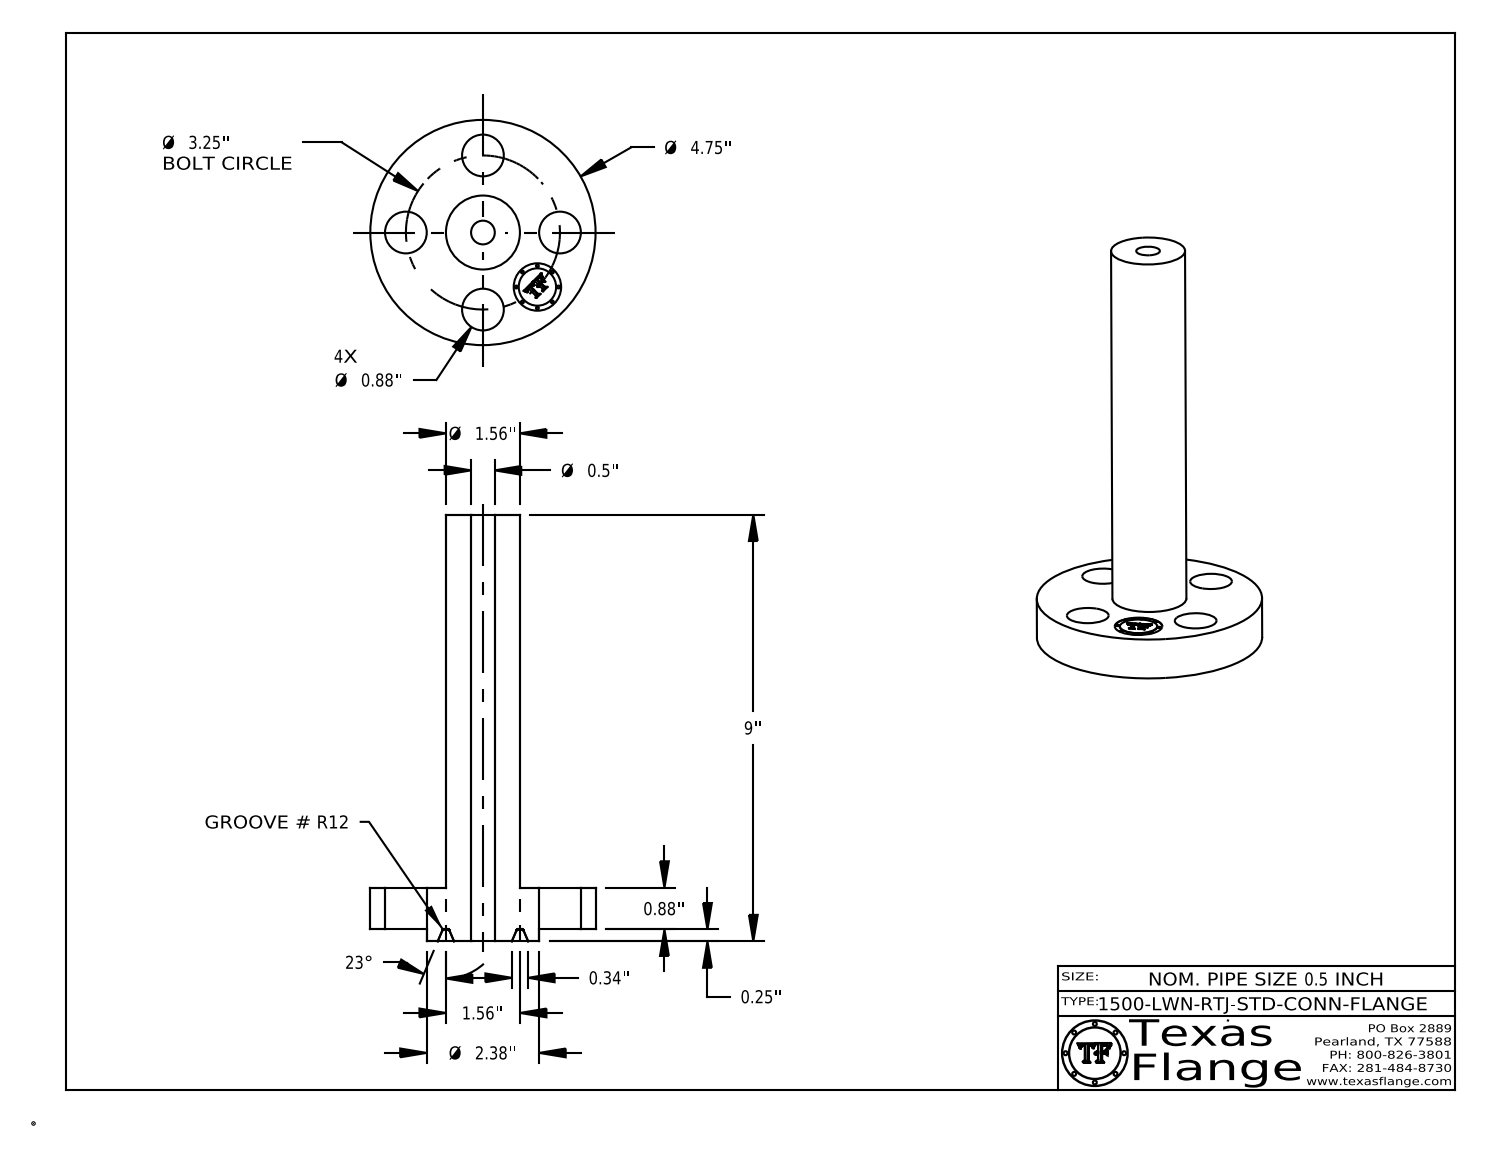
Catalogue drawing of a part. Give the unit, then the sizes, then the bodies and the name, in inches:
Units: inches
Overall size (bounding box): 9 × 4.75 × 4.75
Round holes (diameter × count): ⌀0.88 ×4, ⌀0.5 ×1, ⌀1 ×1
Round bosses / shafts (diameter × count): ⌀0.061 ×8, ⌀4.75 ×1, ⌀2.375 ×1, ⌀1.56 ×1, ⌀0.788 ×1
Main face-to-face distances: 0.88, 0.25, 1.13, 9, 8.75, 7.87, 1.125, 0.875, 7.875, 0.298
Hole centre spacings: 1.625, 2.298, 1.244, 3.003, 3.25
Volume: 27.54 in³ · Surface area: 109.3 in²
Bodies: 1 solid, 419 faces (371 planar, 40 cylindrical, 8 other)
Part name (STEP PRODUCT): 0.5-1500-LWN-RTJ-STD-CONN-FLANGE
STEP written by: CATIA V5 STEP AP214 (AUTOMOTIVE_DESIGN)
